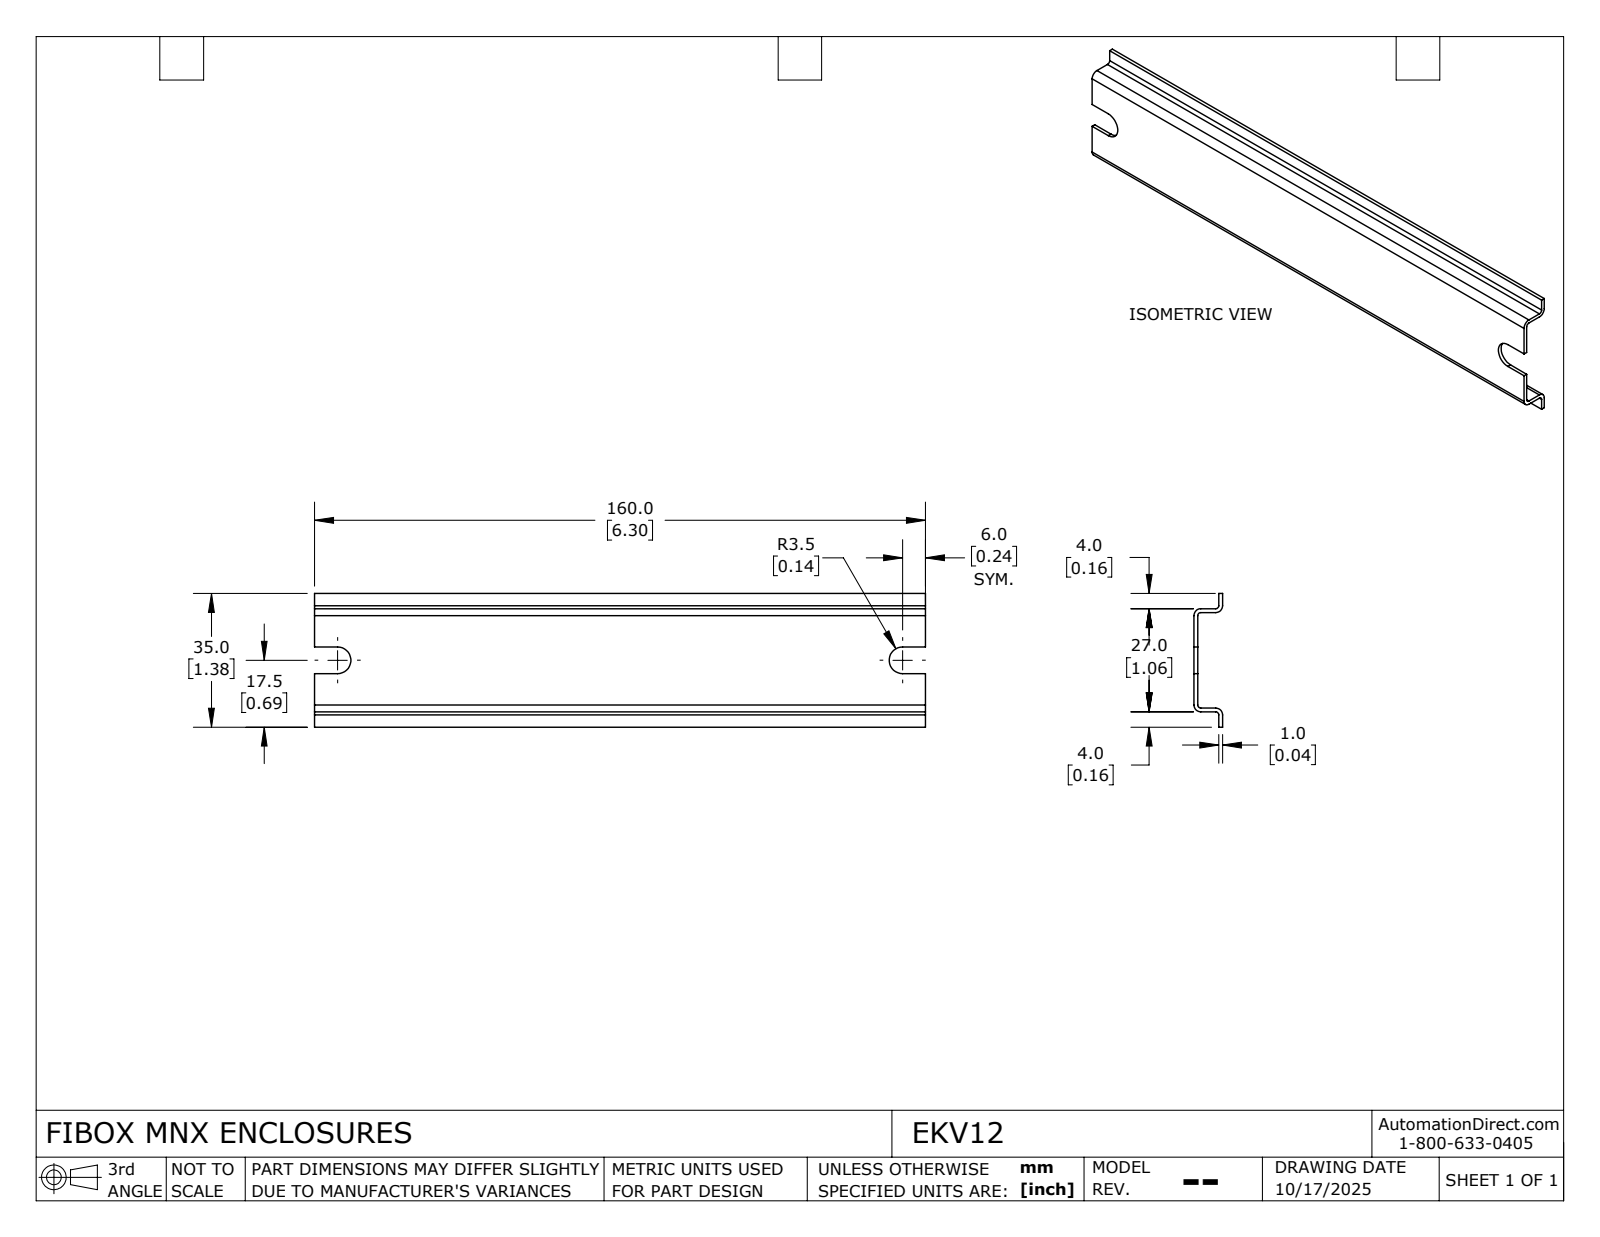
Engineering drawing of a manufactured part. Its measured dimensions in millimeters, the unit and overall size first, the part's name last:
Units: millimetres
Overall size (bounding box): 160 × 35 × 7.5
Partial cylindrical surfaces — rounded edges, fillets, slot ends (radius × count): R0.8 ×4, R1.8 ×4, R3.5 ×2
Main face-to-face distances: 1, 6.5, 26, 7.5, 5.5, 27, 25, 4, 5, 30
Volume: 7 200 mm³ · Surface area: 14 844 mm²
Bodies: 1 solid, 30 faces (20 planar, 10 cylindrical, 0 other)
Part name (STEP PRODUCT): EKV12_Default
STEP written by: SolidWorks 2024 (CONFIG_CONTROL_DESIGN)
